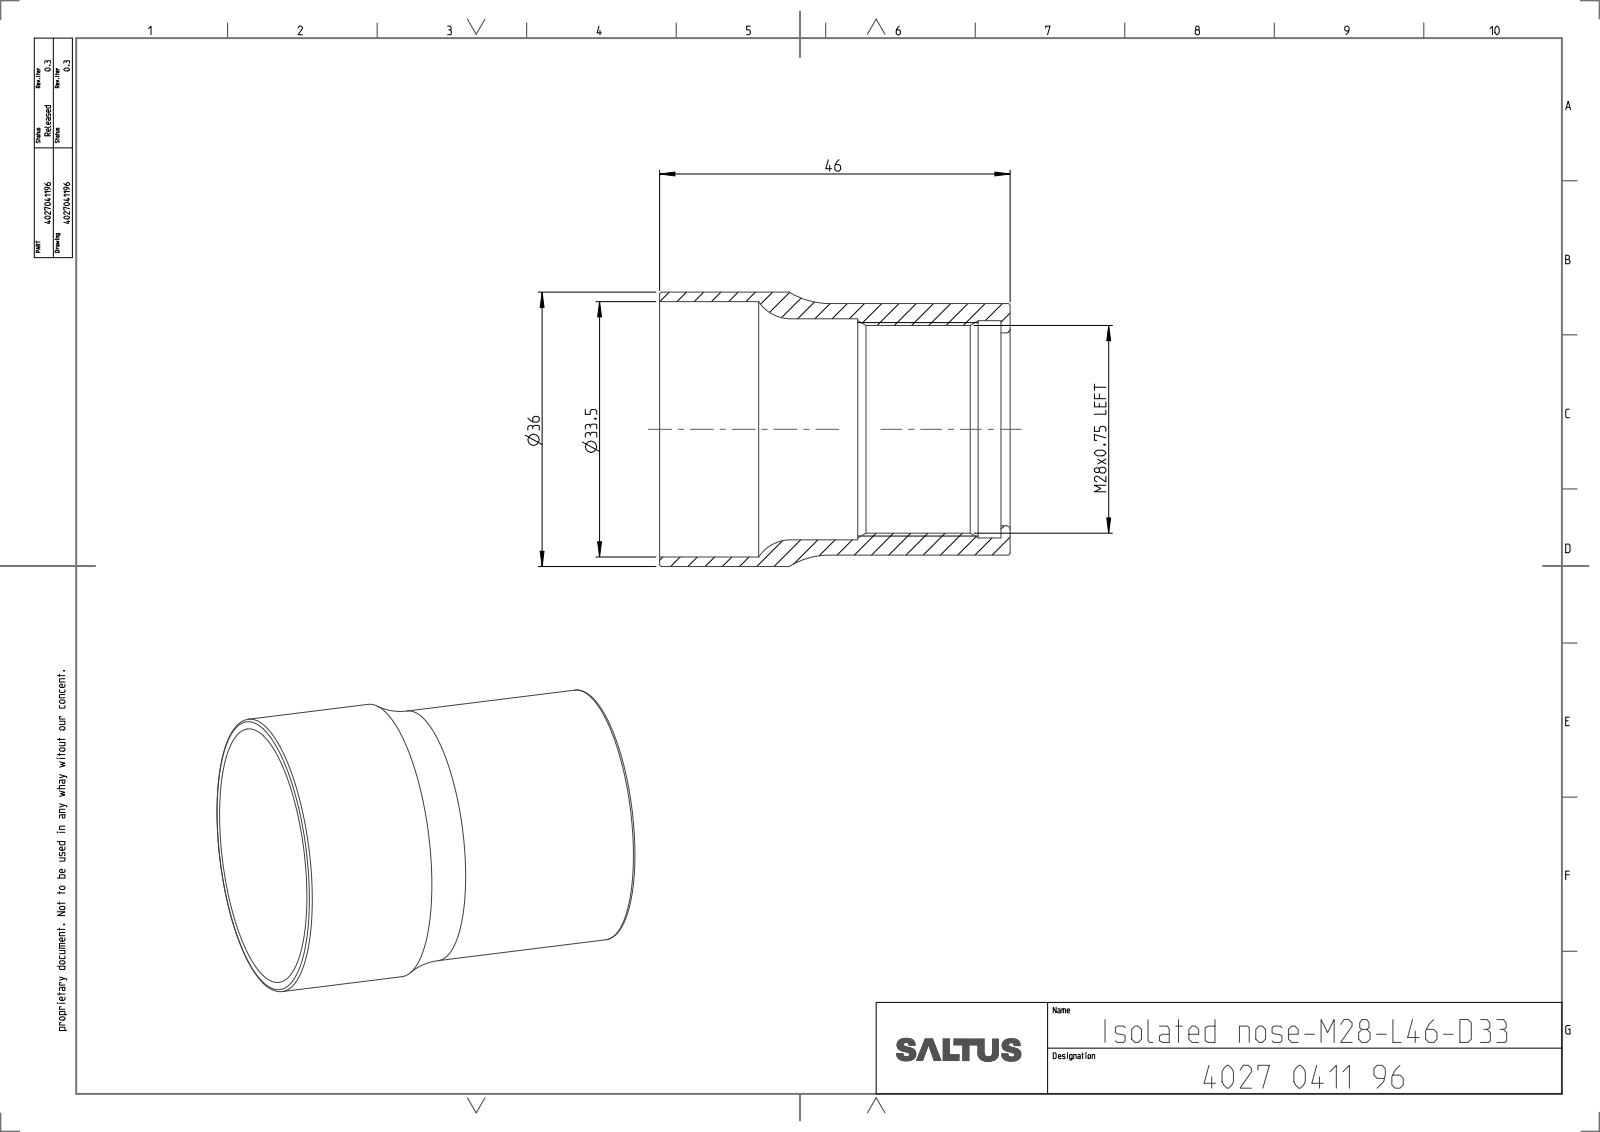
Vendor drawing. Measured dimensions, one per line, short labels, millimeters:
name: 4027041196
written by: CREO PARAMETRIC BY PTC INC, 2022414 (CONFIG_CONTROL_DESIGN)
unit: mm
bodies: 1 solid, 35 faces (5 planar, 16 cylindrical, 14 other)
size: 46 × 36 × 36
volume: 10 273 mm³; area: 11 366 mm²
holes: 1× ⌀25.3, 1× ⌀27.25, 1× ⌀28.5, 1× ⌀29, 1× ⌀33.5
bosses: 1× ⌀36, 1× ⌀33, 1× ⌀28
face distances: 1.2, 46, 44.8, 20, 18.8, 26, 4.2, 3, 15.8, 41.8
